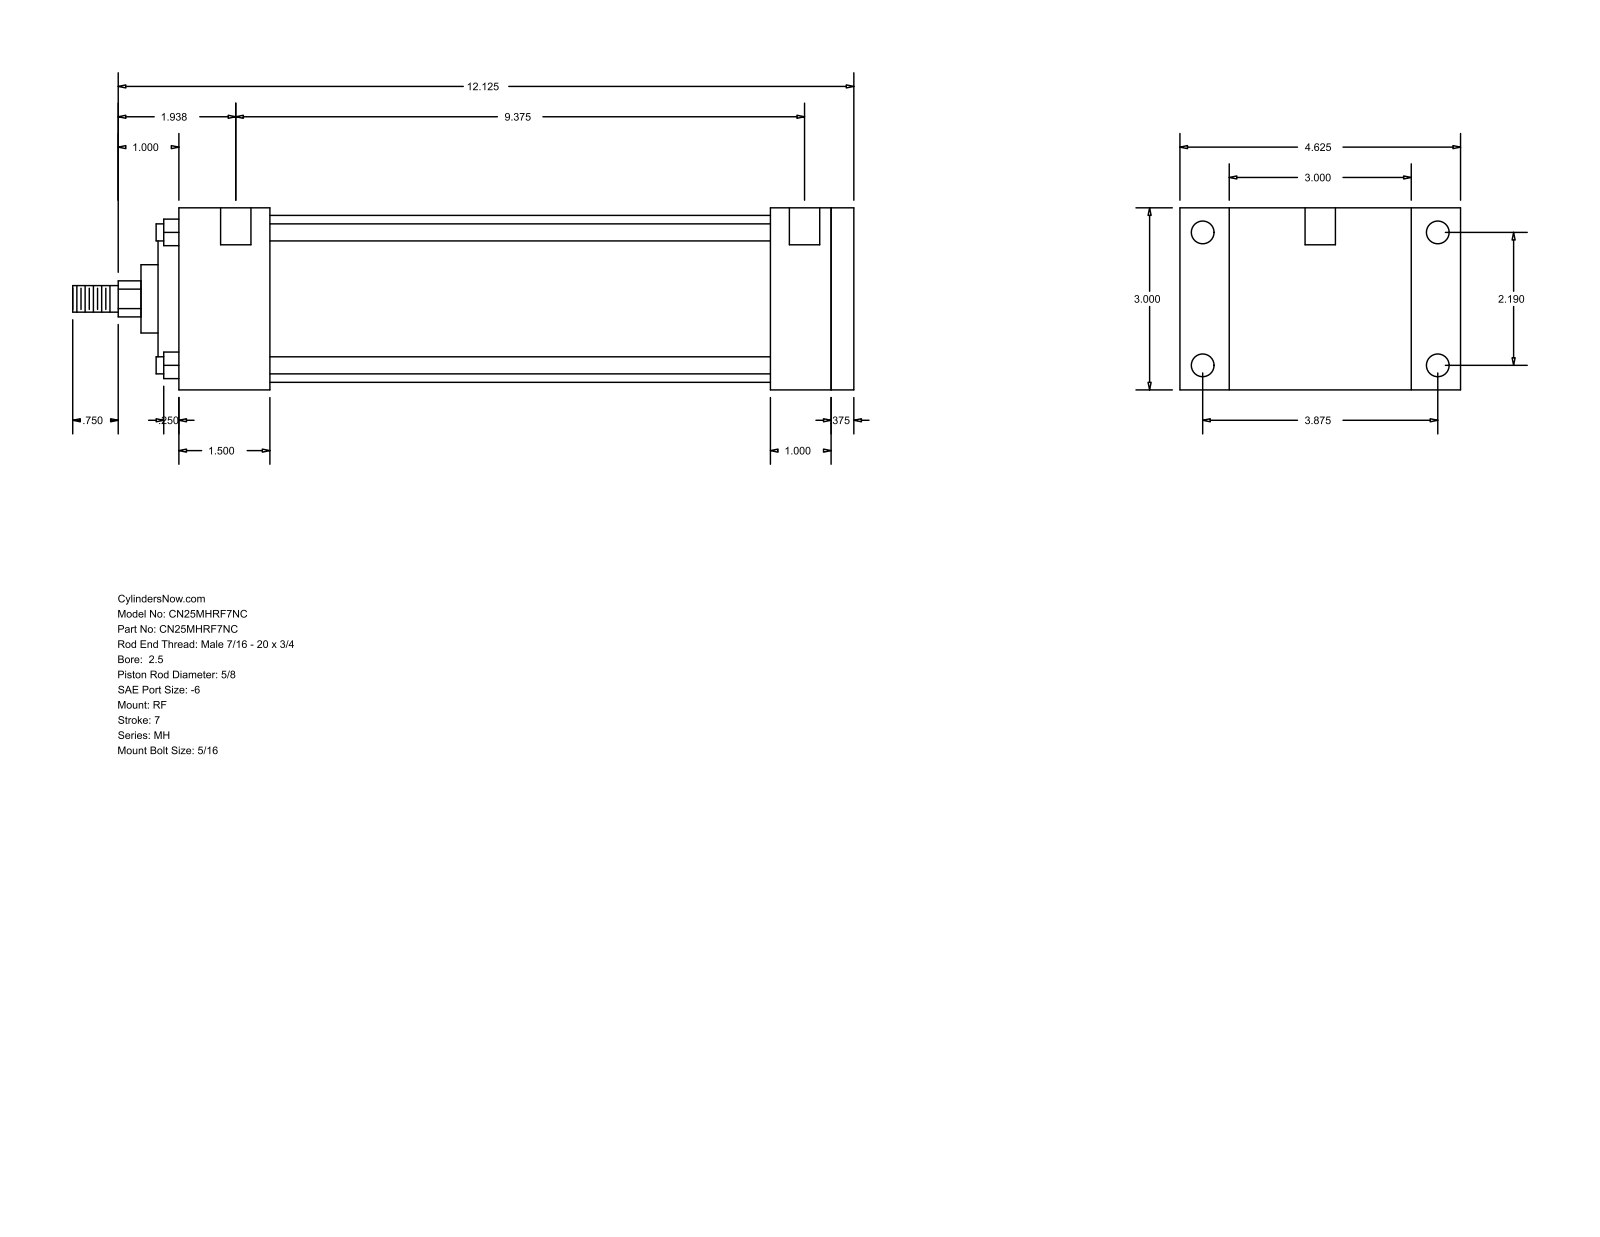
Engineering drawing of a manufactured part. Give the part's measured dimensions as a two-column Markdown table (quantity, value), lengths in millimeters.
| quantity | value |
| --- | --- |
| part name | MH_RF__0250_0.625 |
| STEP written by | GSSL Pune (CONFIG_CONTROL_DESIGN) |
| units | millimeters |
| bodies | 0 solids, 94 faces (65 planar, 29 cylindrical, 0 other) |
| overall size | 327.02 × 117.47 × 76.2 |
| round holes (diameter × count) | 5.56 × 4, 9.53 × 4, 12.7 × 2 |
| round bosses / shafts (diameter × count) | 7.14 × 4, 69.85 × 1, 55.55 × 1, 28.57 × 1, 15.88 × 1, 11.11 × 1 |
| partial cylindrical surfaces (radius × count) | 7.54 × 1 |
| main face-to-face distances | 76.2, 9.53, 282.58, 273.05, 25.4, 34.93, 38.1, 247.65, 209.55, 234.95 |
| hole center spacings | 55.62, 98.42, 113.05, 246.06, 3.17, 4.76, 238.13, 241.3 |
